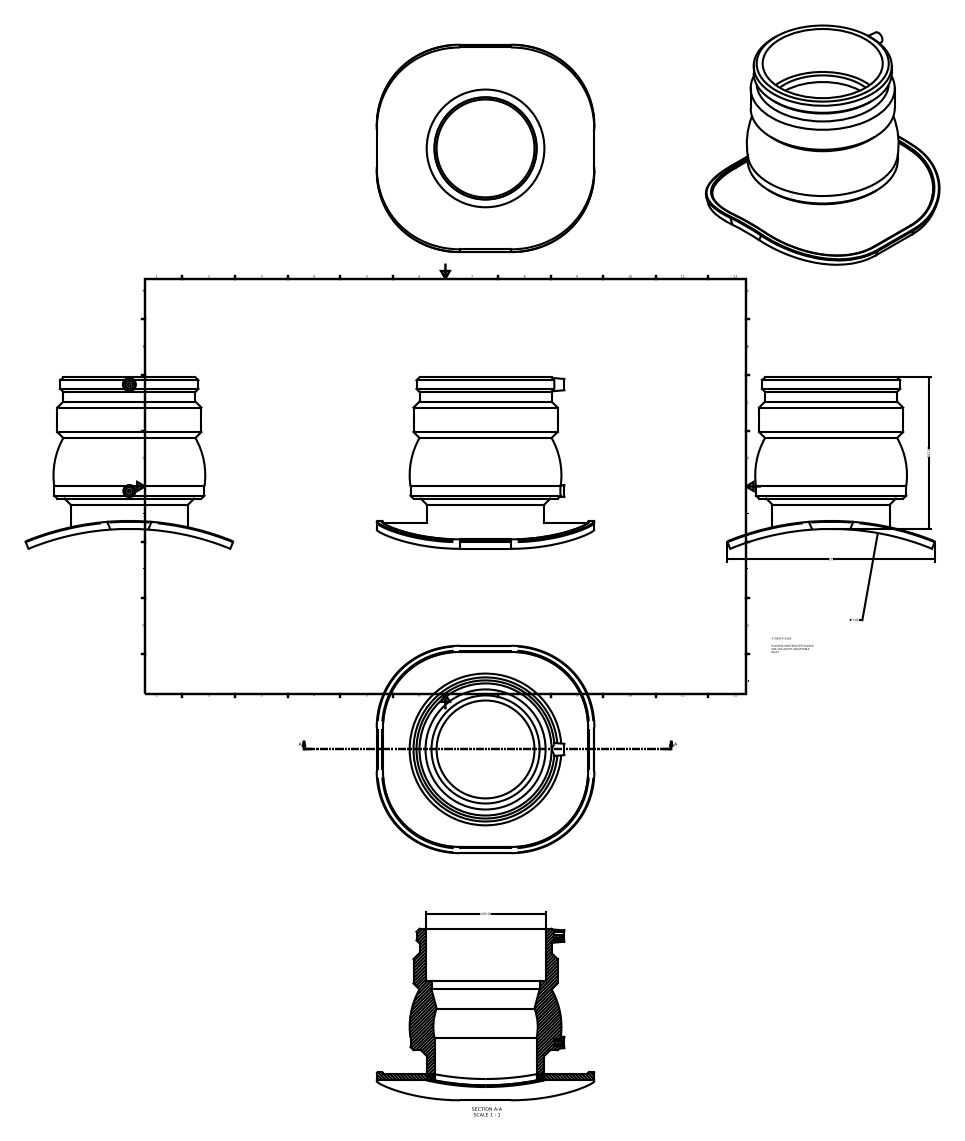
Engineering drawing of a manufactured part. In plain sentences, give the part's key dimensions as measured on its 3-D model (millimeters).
The part is named "475804710160". Its 3-D file was written by "Autodesk Inventor 2015 (AUTOMOTIVE_DESIGN)". It is 2 solids with 69 faces: 17 planar, 29 cylindrical and 23 other. Overall it measures 290 by 276.32 by 228.45 millimeters. Its volume is 2 571 000 cubic millimeters and its surface area 370 078 square millimeters. Round holes: 2 of diameter 10, 1 of diameter 136, 1 of diameter 144, 1 of diameter 160. Round bosses or shafts: 2 of diameter 4, 1 of diameter 200, 1 of diameter 192, 1 of diameter 184, 1 of diameter 176, 1 of diameter 156.8. Partial cylindrical surfaces (rounded edges, fillets, slot ends): 4 of radius 1.11, 4 of radius 102.49, 4 of radius 110.8, 1 of radius 355, 1 of radius 363.31, 1 of radius 365.65. The main face-to-face distances are 161.6, 91.6, 70, 290, 8.31, 250, 40, 281.69, 236, 14. The hole center spacings are 141.82.
